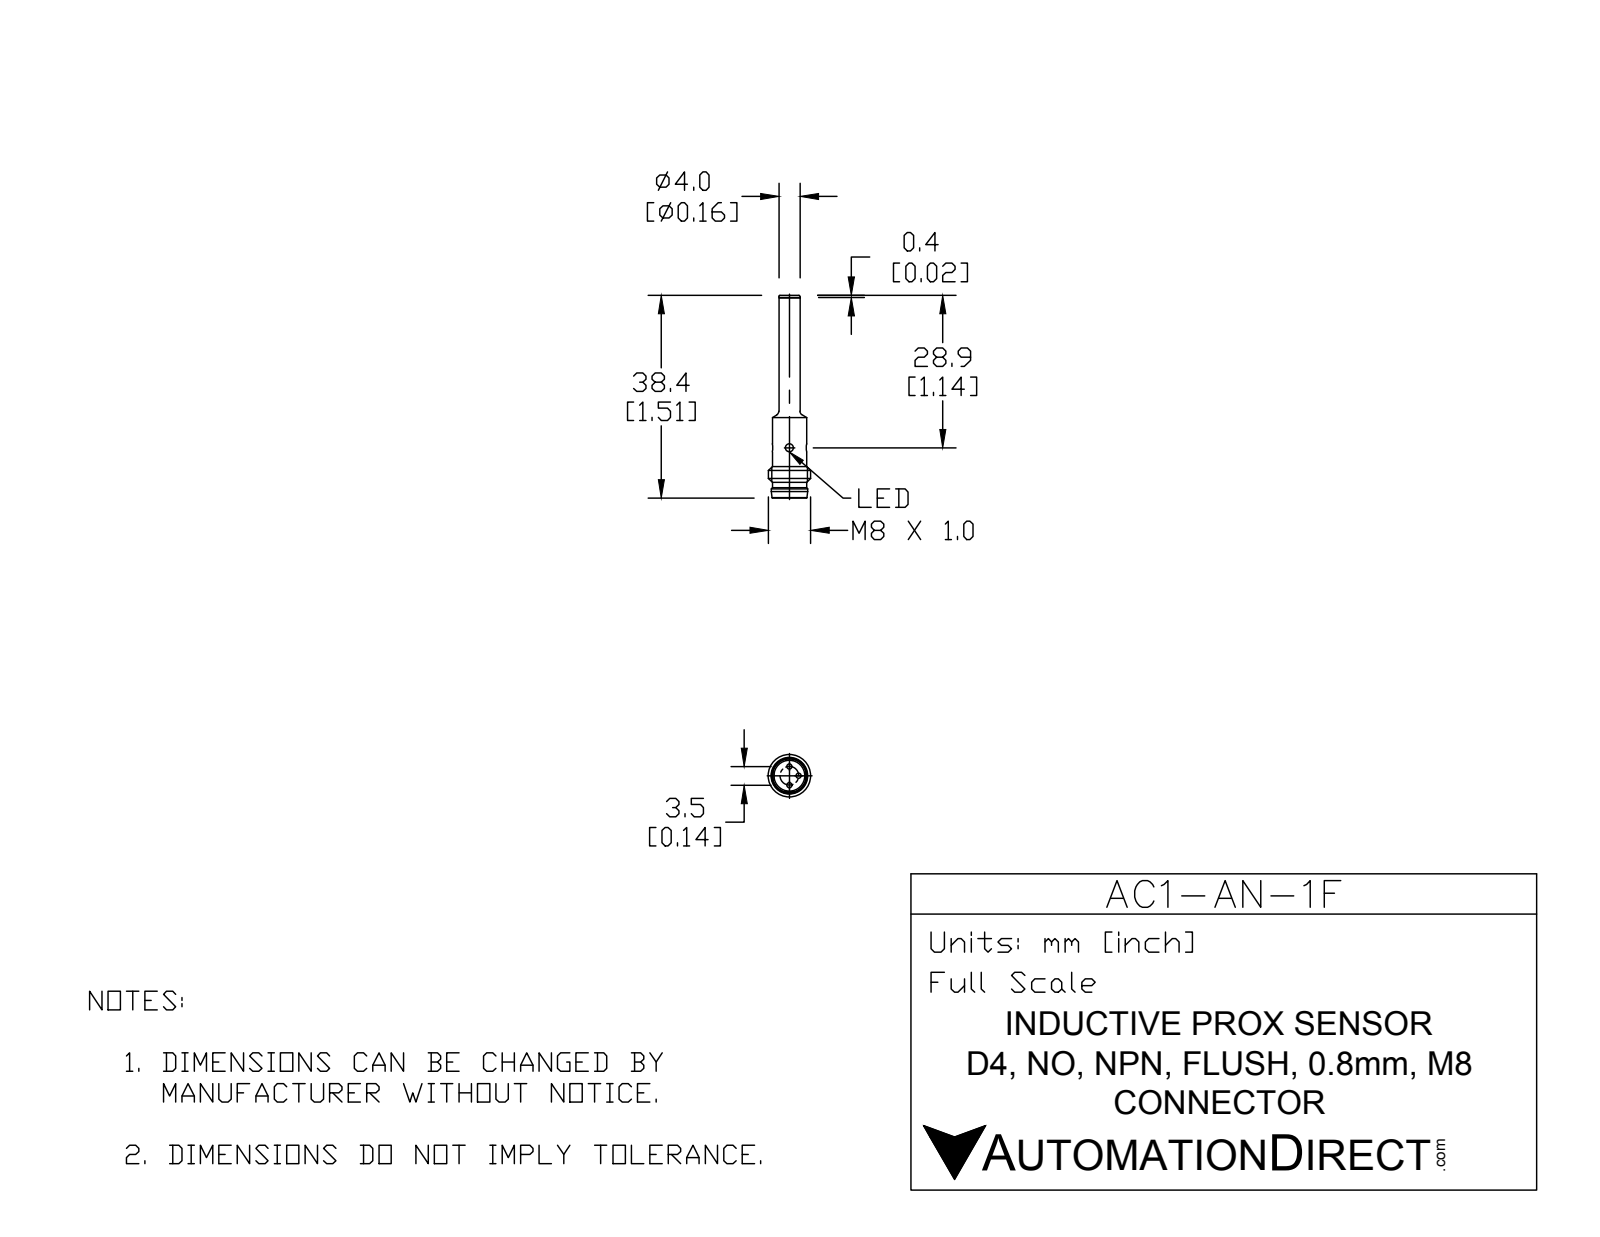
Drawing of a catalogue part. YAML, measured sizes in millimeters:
part_name: "AC1-AN-1F"
step_written_by: "SolidWorks 2015 (CONFIG_CONTROL_DESIGN)"
units: millimeters
bodies: {solids: 4, faces: 59, planar: 11, cylindrical: 26, other: 22}
overall_size: [38.4, 8, 8]
volume: 757
surface_area: 840
round_holes:
  - {diameter: 1.5, count: 2}
  - {diameter: 5.85, count: 1}
round_bosses_or_shafts:
  - {diameter: 1, count: 3}
  - {diameter: 8, count: 1}
  - {diameter: 6.9, count: 1}
  - {diameter: 6.5, count: 1}
  - {diameter: 4, count: 1}
face_to_face_distances: [33.4, 5.5, 5, 38.4, 38, 33, 0.4]
